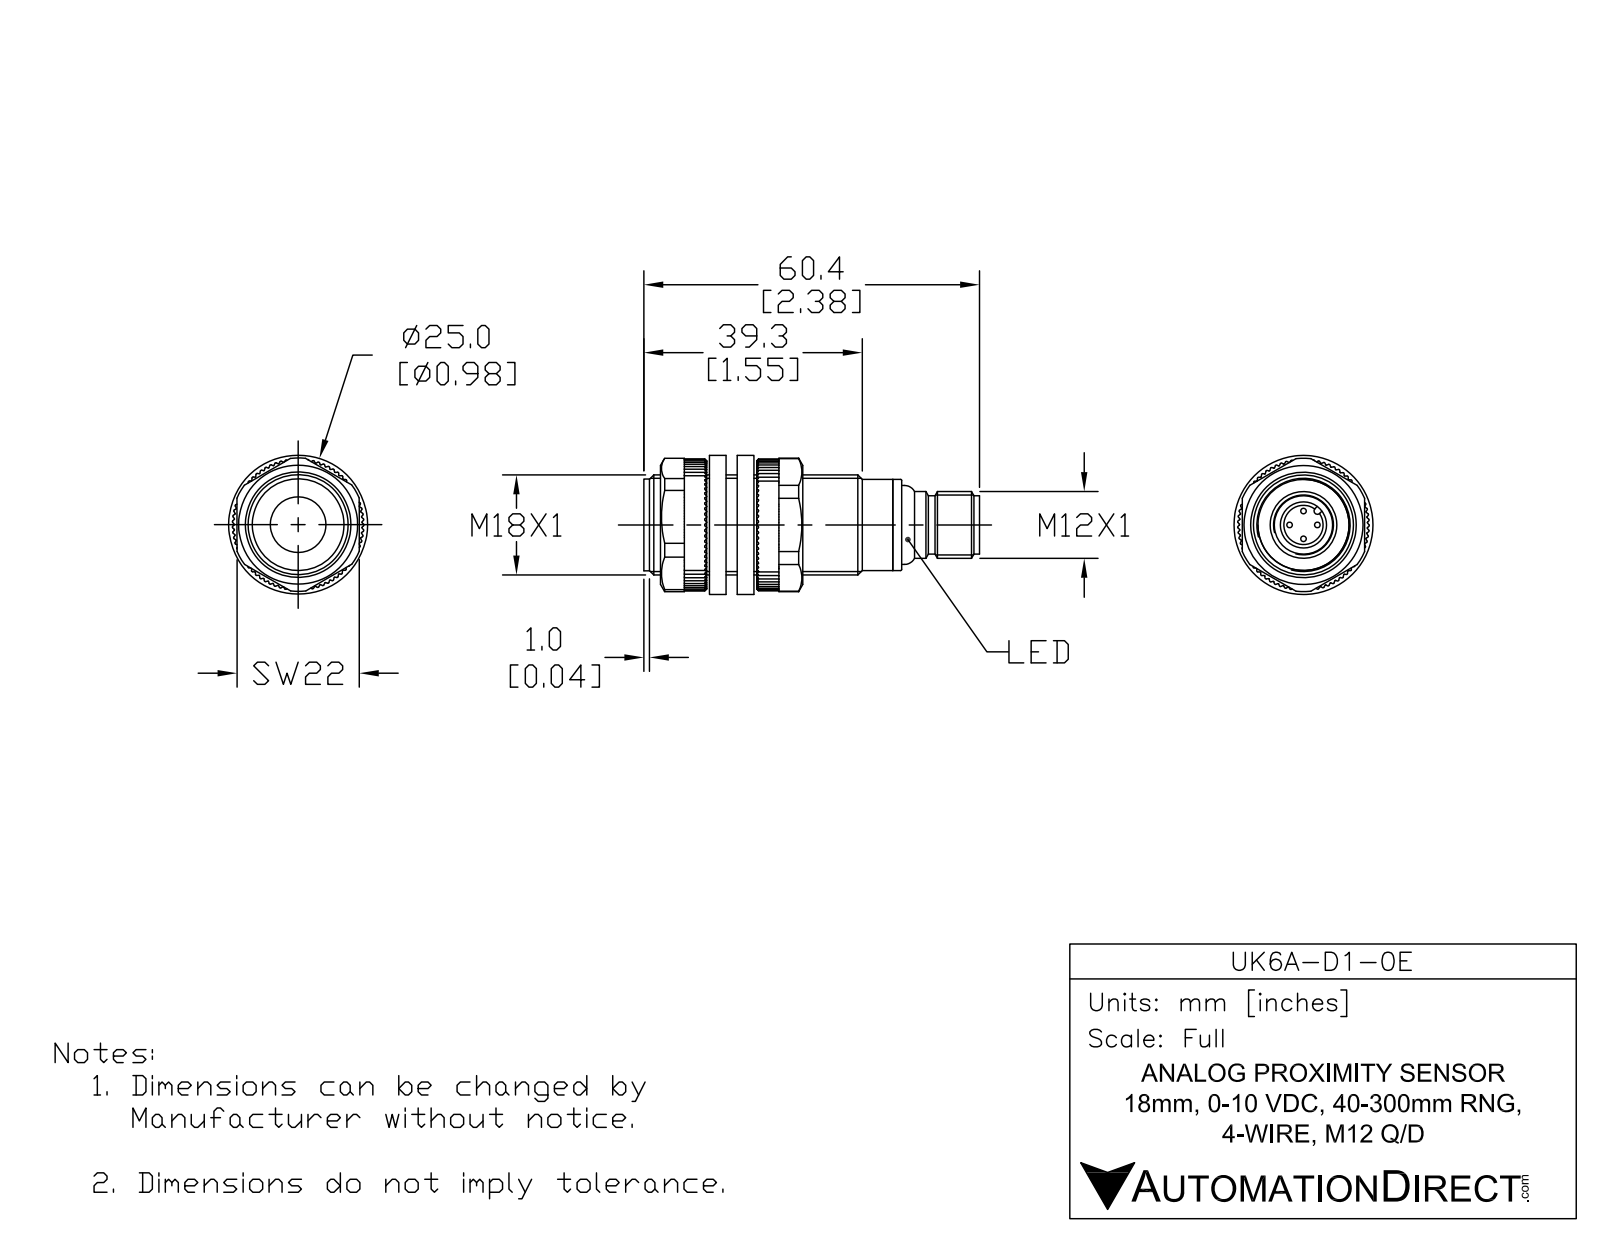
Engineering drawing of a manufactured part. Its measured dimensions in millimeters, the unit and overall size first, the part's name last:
Units: millimetres
Overall size (bounding box): 60.3 × 18 × 18
Round holes (diameter × count): ⌀7 ×1, ⌀8.3 ×1, ⌀9.5 ×1
Round bosses / shafts (diameter × count): ⌀1 ×4, ⌀18 ×1, ⌀16.4 ×1, ⌀15.8 ×1, ⌀14.2 ×1, ⌀12 ×1, ⌀10.5 ×1
Partial cylindrical surfaces — rounded edges, fillets, slot ends (radius × count): R0.6 ×1
Main face-to-face distances: 43.8, 1, 44.8, 1, 44.8, 46.3, 46.3, 45.3, 1.5, 51.4
Volume: 12 400 mm³ · Surface area: 4 934 mm²
Bodies: 4 solids, 86 faces (15 planar, 36 cylindrical, 35 other)
Part name (STEP PRODUCT): UK6A-D1-0E
STEP written by: SolidWorks 2017 (AUTOMOTIVE_DESIGN)
